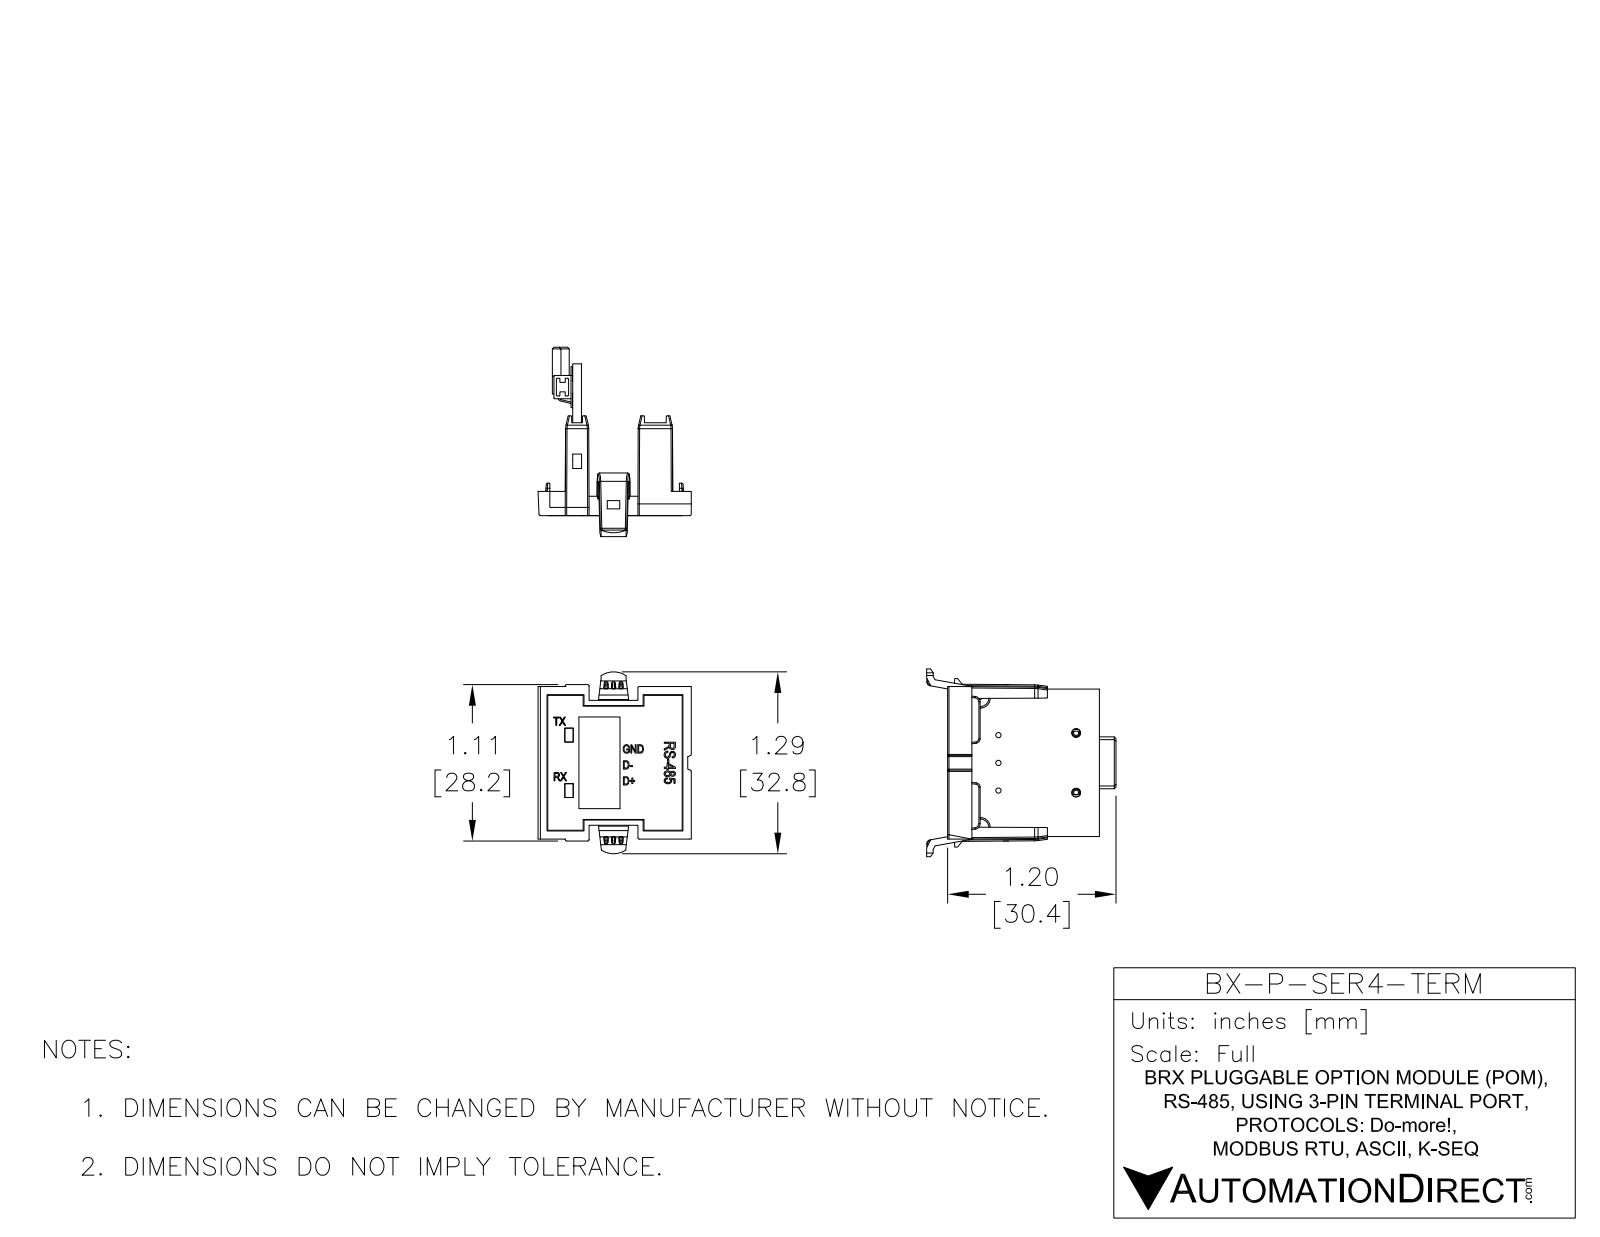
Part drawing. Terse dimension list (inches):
name: BX-P-SER4-TERM
written by: SolidWorks 2016 (AUTOMOTIVE_DESIGN)
unit: in
bodies: 54 solids, 2196 faces (1655 planar, 403 cylindrical, 138 other)
size: 1.612 × 1.334 × 1.084
volume: 0.315 in³; area: 14.43 in²
holes: 3× ⌀0.01, 3× ⌀0.037, 3× ⌀0.039, 3× ⌀0.079, 3× ⌀0.11, 2× ⌀0.063
bosses: 3× ⌀0.102, 3× ⌀0.01
rounds: 89× R0.004, 47× R0.008, 10× R0.033, 8× R0.006, 6× R0.012, 6× R0.014, 5× R0.016, 5× R0.049
face distances: 0.062, 0.062, 0.02, 0.066, 0.276, 0.138, 0.066, 0.118, 0.332, 0.14
hole spacings: 0.138, 0.552, 0.569, 0.276, 0.557, 0.617, 1.107, 1.125
